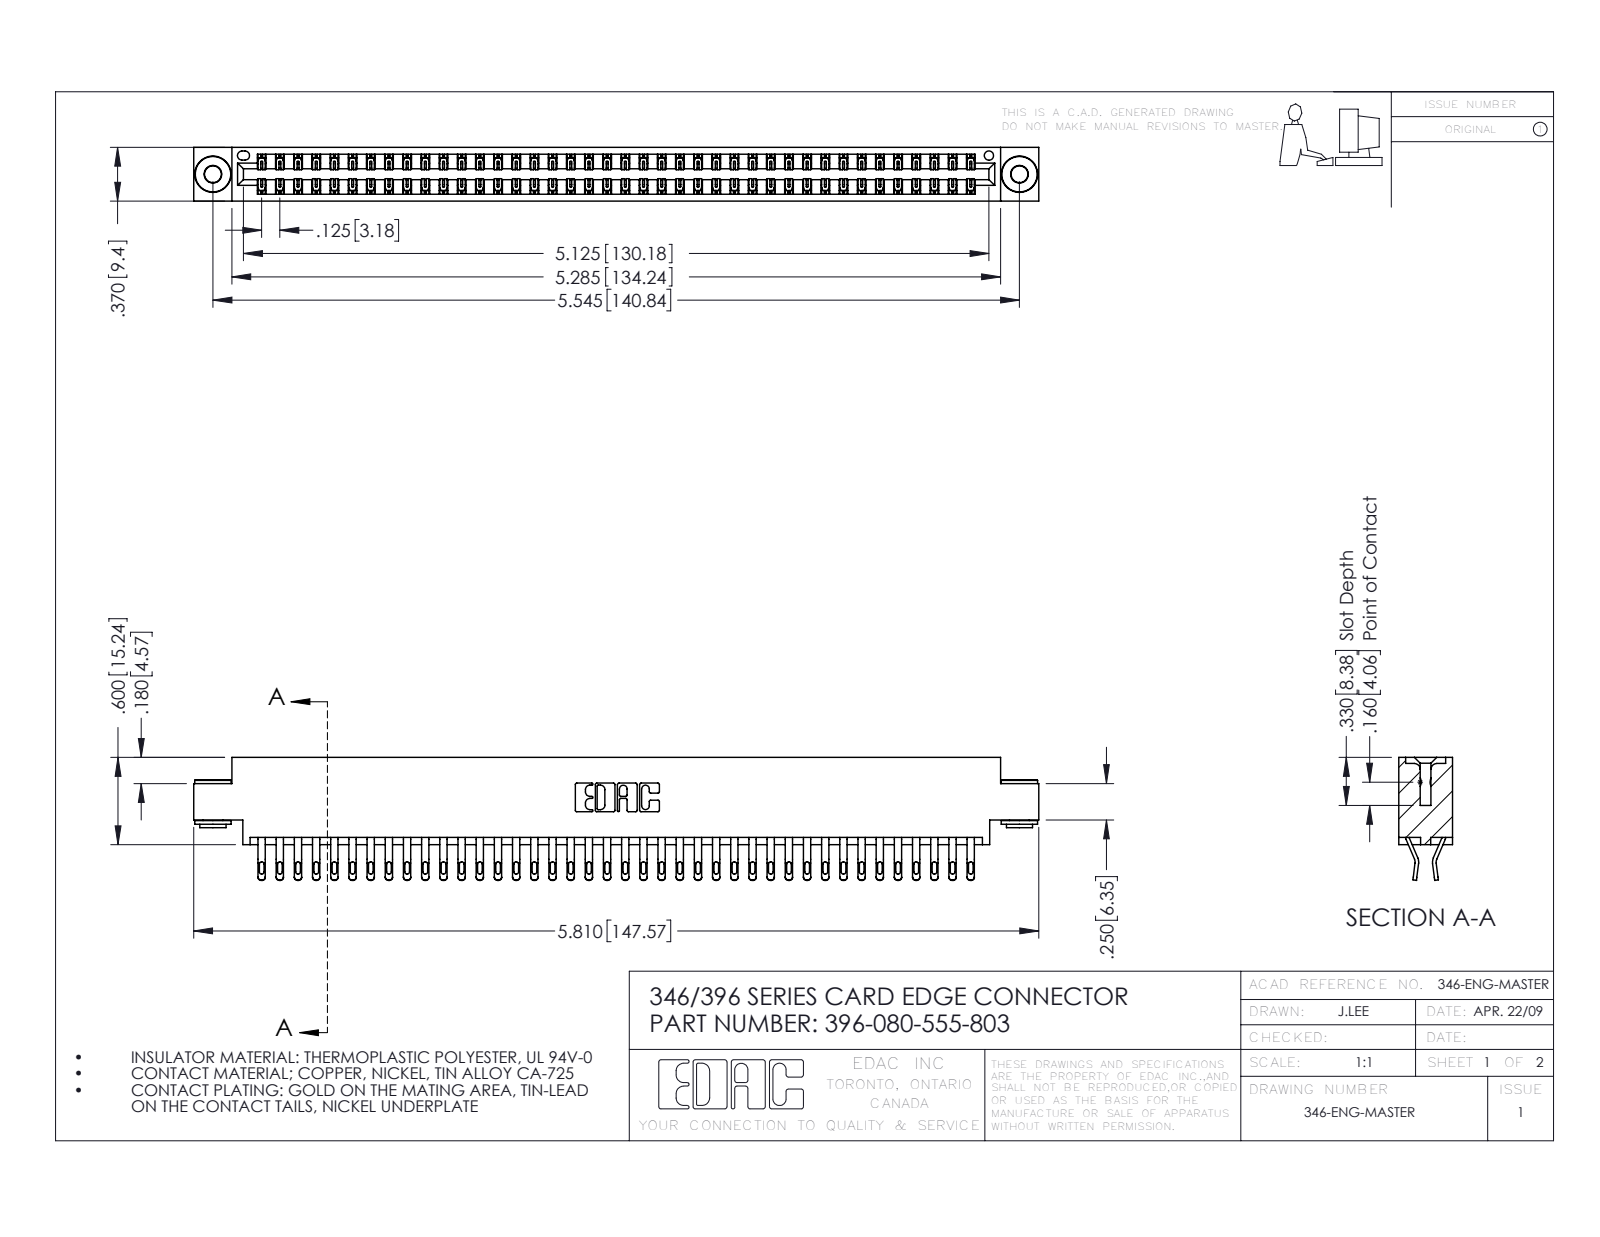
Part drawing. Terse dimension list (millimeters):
name: 346 Part_0.170 Offset - 0.156 Dia-TH; 345-292-001_555 Tail; 396-080-555-803; 345-250-002_345-250-002-102
written by: SolidWorks 2016 (CONFIG_CONTROL_DESIGN)
unit: mm
bodies: 83 solids, 4804 faces (2730 planar, 2066 cylindrical, 8 other)
size: 147.6 × 21.5 × 9.4
volume: 14 500 mm³; area: 21 080 mm²
holes: 2× ⌀2.9, 2× ⌀4, 1× ⌀1.6
bosses: 2× ⌀6.4, 2× ⌀4.6, 2× ⌀3.5
rounds: 160× R0.4, 160× R0.5, 120× R0.2, 22× R0.3, 6× R0.2, 6× R0.8, 3× R0.7, 2× R0.3
face distances: 1.2, 8.2, 9.4, 6.4, 0.6, 7, 1.8, 7.6, 3.8, 5.6
hole spacings: 6.2, 135.5, 140.8
